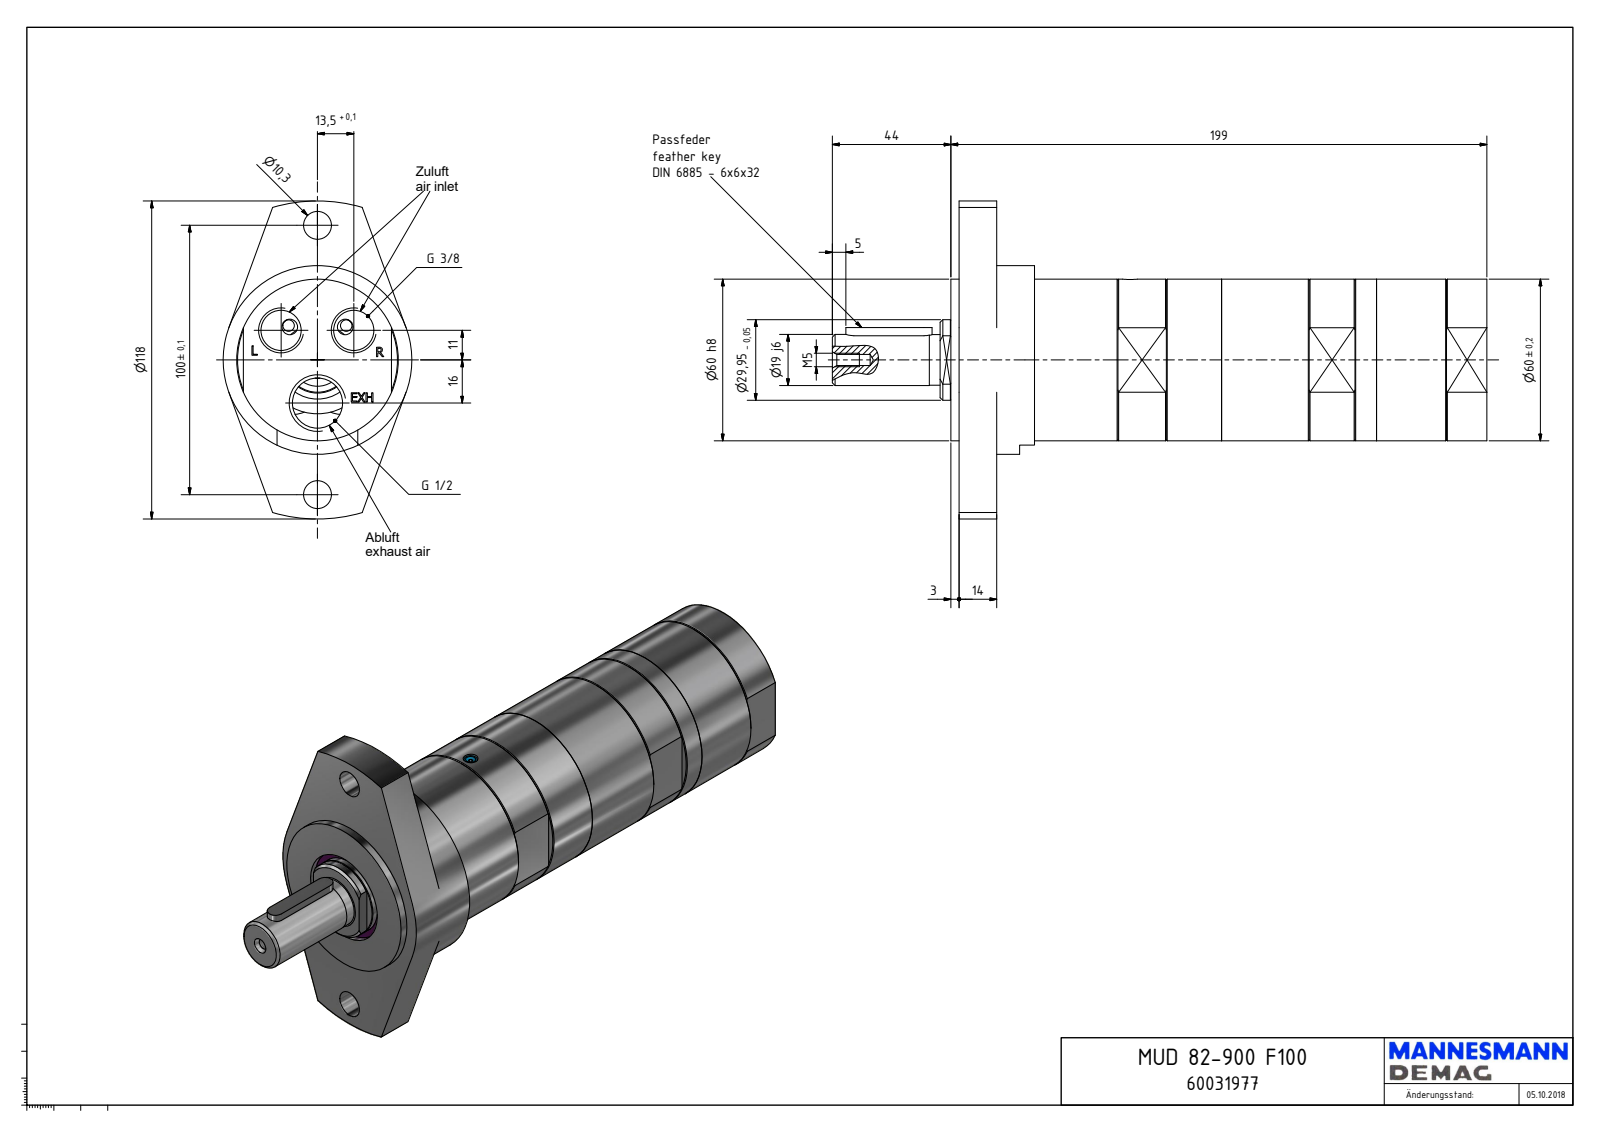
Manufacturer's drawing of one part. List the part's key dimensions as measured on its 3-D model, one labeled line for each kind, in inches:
Part name (STEP PRODUCT): MUD 82-425 F100_60031977
STEP written by: Autodesk Inventor 2018 (AUTOMOTIVE_DESIGN)
Units: inches
Bodies: 1 solid, 200 faces (114 planar, 47 cylindrical, 39 other)
Overall size (bounding box): 9.567 × 4.646 × 2.756
Volume: 37.62 in³ · Surface area: 96.6 in²
Round holes (diameter × count): ⌀0.406 ×2, ⌀0.589 ×2, ⌀0.061 ×1, ⌀0.157 ×1, ⌀0.163 ×1, ⌀0.217 ×1, ⌀0.733 ×1, ⌀1.378 ×1
Round bosses / shafts (diameter × count): ⌀2.756 ×1, ⌀2.362 ×1, ⌀2.172 ×1, ⌀1.179 ×1, ⌀0.748 ×1, ⌀0.74 ×1, ⌀0.197 ×1, ⌀0.142 ×1
Partial cylindrical surfaces — rounded edges, fillets, slot ends (radius × count): R0.118 ×2, R0.295 ×2, R0.335 ×1, R0.778 ×1, R0.925 ×1, R1.061 ×1, R2.323 ×1
Main face-to-face distances: 0.551, 0.669, 0.118, 7.717, 7.165, 7.835, 2.165, 1.22, 1.102, 6.614
Hole centre spacings: 0.685, 1.189, 1.625, 1.969, 2.46, 0.63, 1.063, 1.339
